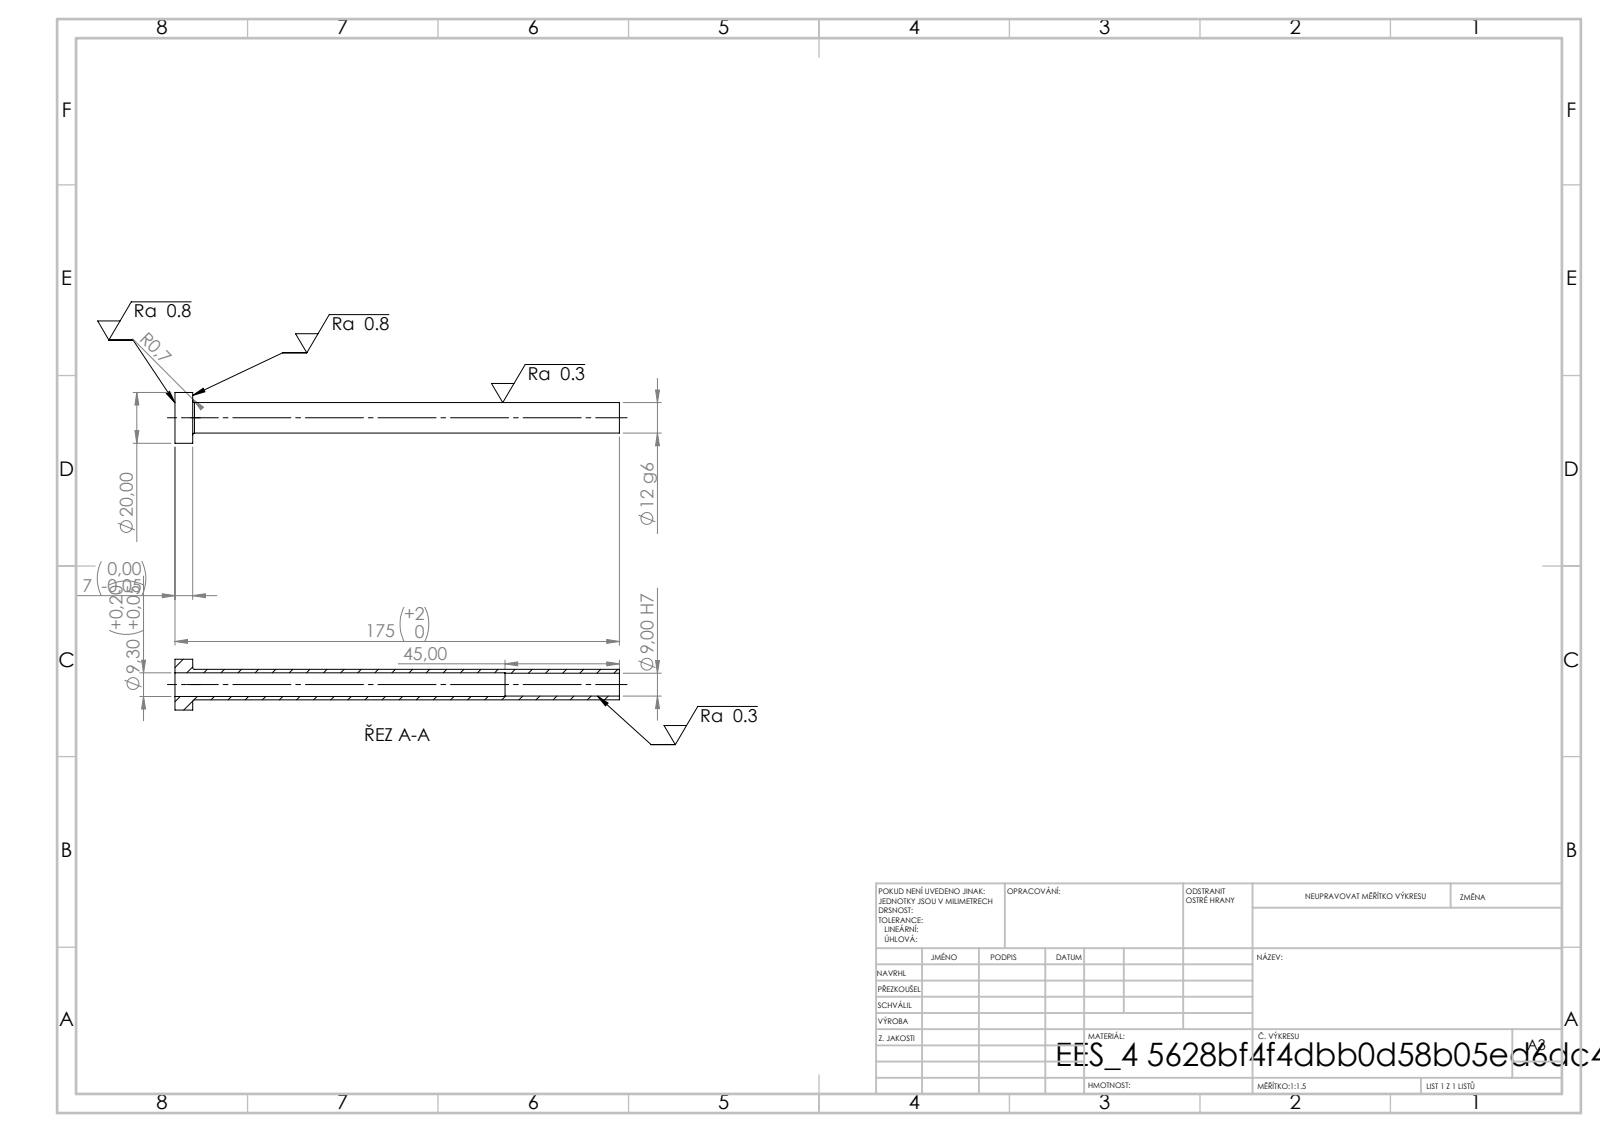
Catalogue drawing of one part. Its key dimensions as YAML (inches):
step_written_by: "SolidWorks 2019 (CONFIG_CONTROL_DESIGN)"
units: inches
bodies: {solids: 1, faces: 14, planar: 4, cylindrical: 8, other: 2}
overall_size: [6.89, 0.787, 0.787]
volume: 0.58
surface_area: 19.12
round_holes:
  - {diameter: 0.354, count: 1}
  - {diameter: 0.366, count: 1}
round_bosses_or_shafts:
  - {diameter: 0.787, count: 1}
  - {diameter: 0.472, count: 1}
face_to_face_distances: [0.276, 6.89, 6.614, 5.118, 4.843, 1.772]
